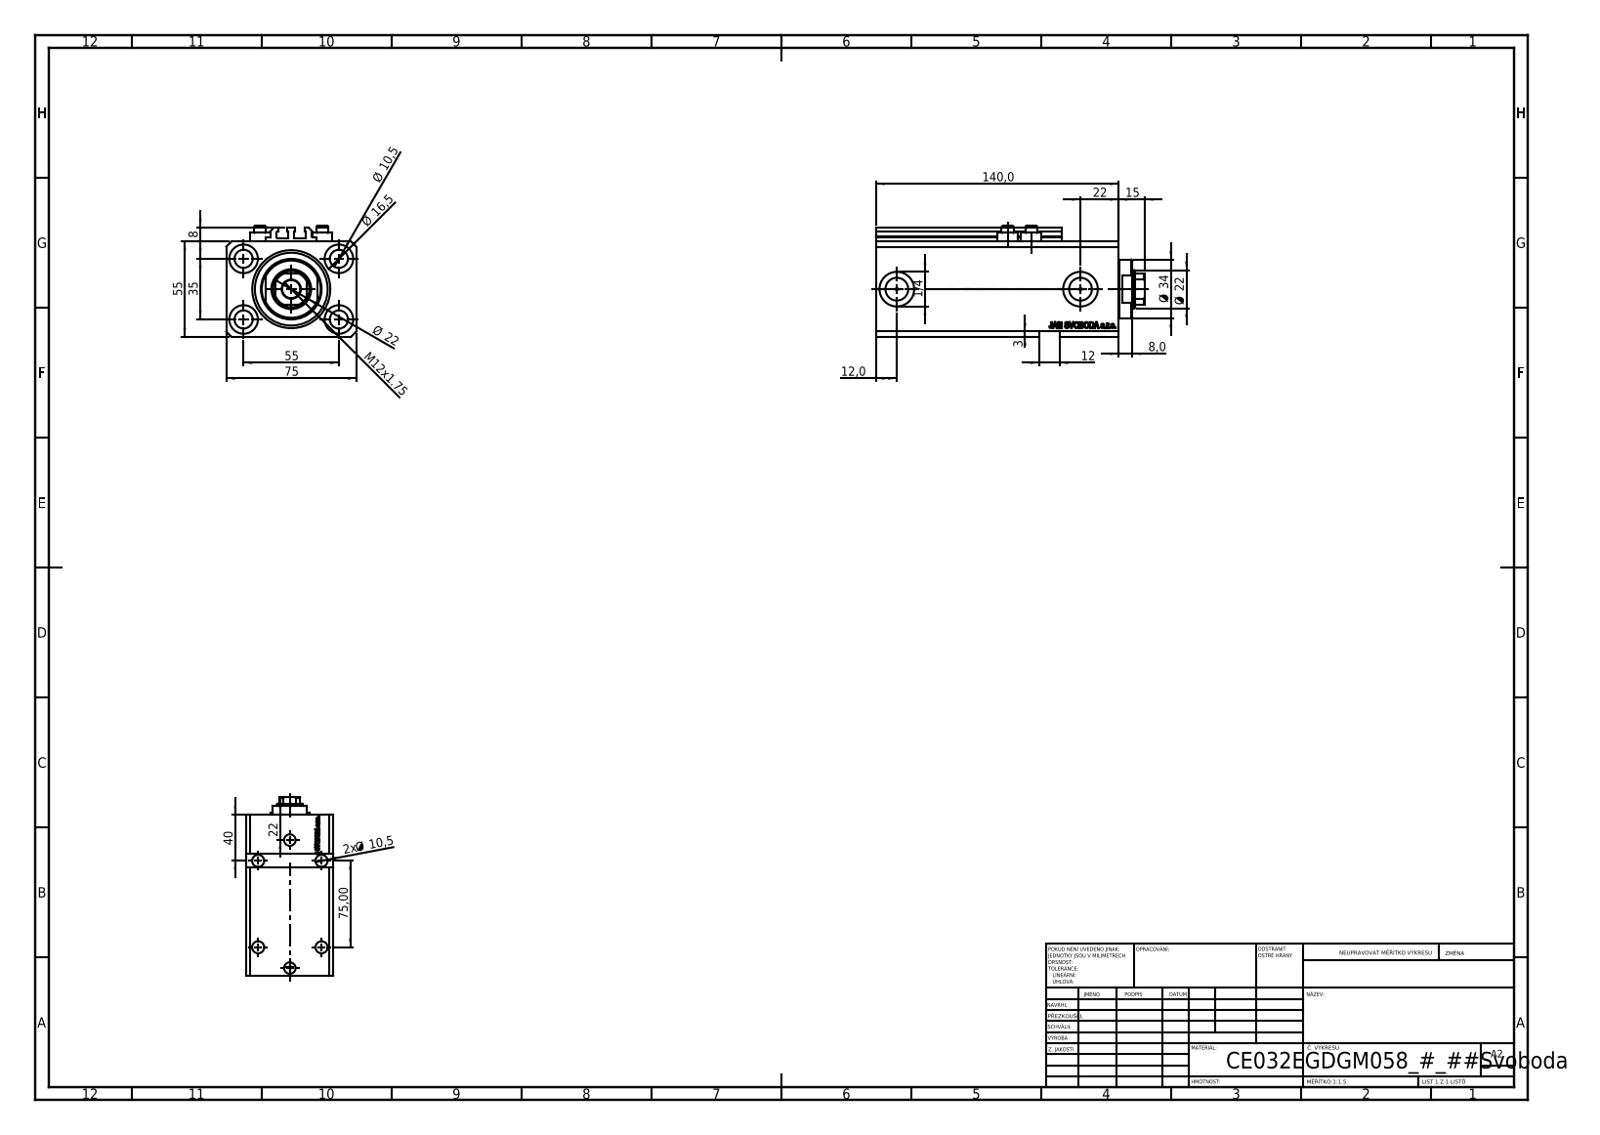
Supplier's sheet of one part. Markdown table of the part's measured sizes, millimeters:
| quantity | value |
| --- | --- |
| part name | V250CE_C_VCP; V250CE_E_Body; ALLEN BOLT V250CE; V250CE_VC_E |
| STEP written by | SolidWorks 2019 (CONFIG_CONTROL_DESIGN) |
| units | millimeters |
| bodies | 8 solids, 1100 faces (518 planar, 158 cylindrical, 424 other) |
| overall size | 155 × 75 × 64 |
| volume | 481 599 mm³ |
| surface area | 116 451 mm² |
| round holes (diameter × count) | 10.5 × 9, 1.25 × 4, 4 × 4, 16.5 × 4, 10 × 2, 13.16 × 2, 20 × 2, 22 × 1, 32 × 1, 45 × 1 |
| round bosses / shafts (diameter × count) | 11.6 × 4, 7 × 4, 34 × 1 |
| partial cylindrical surfaces (radius × count) | 0.2 × 10, 10.5 × 1 |
| main face-to-face distances | 55, 75, 15, 9.9, 140, 125, 3, 57, 115.1, 130.1 |
| hole center spacings | 32.6, 32.87, 55, 96.98, 13.6, 14.09, 25.81, 32.58 |
